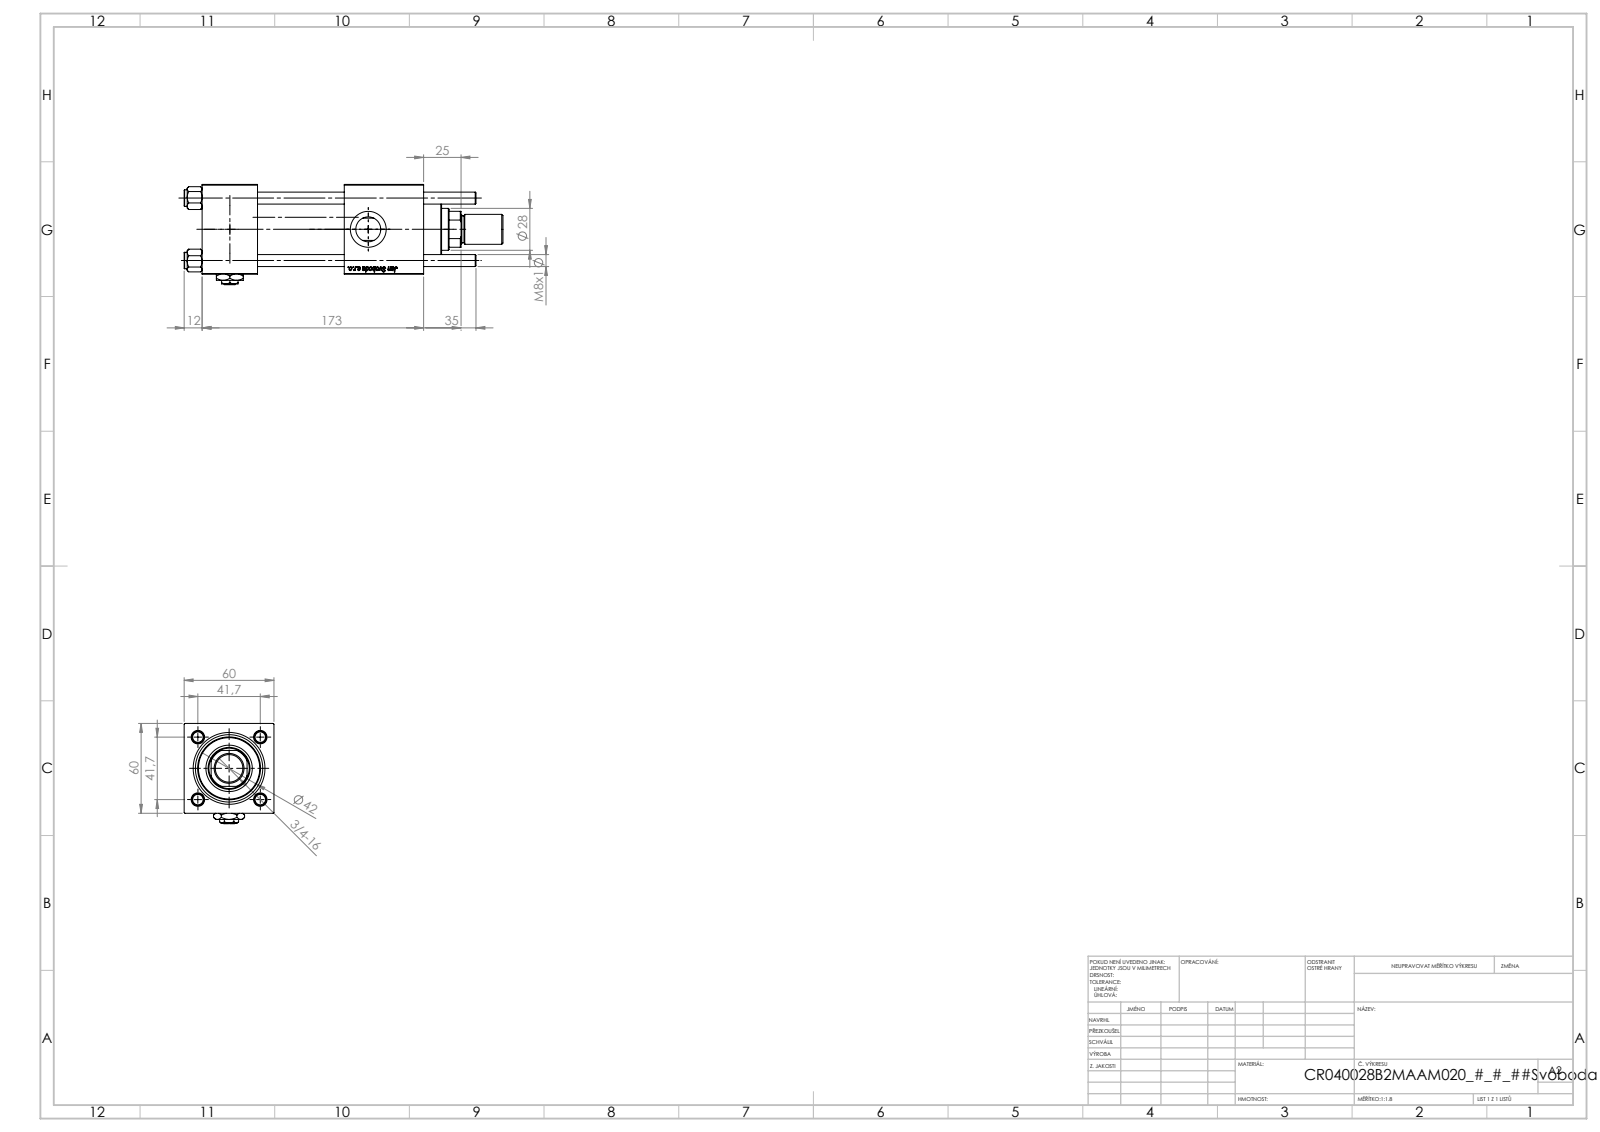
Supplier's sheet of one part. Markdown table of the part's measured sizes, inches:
| quantity | value |
| --- | --- |
| part name | Zatka_pro_OIL_PORT; V215CR_VCP_B; ROD_END_AH; V215CR_B-1 (+3 more) |
| STEP written by | SolidWorks 2019 (CONFIG_CONTROL_DESIGN) |
| units | inches |
| bodies | 13 solids, 1226 faces (460 planar, 90 cylindrical, 676 other) |
| overall size | 8.386 × 2.638 × 2.362 |
| volume | 26.98 in³ |
| surface area | 192.4 in² |
| round holes (diameter × count) | 0.315 × 4, 0.276 × 2, 0.656 × 2, 0.945 × 2, 0.63 × 1, 0.728 × 1, 1.102 × 1, 1.22 × 1, 1.575 × 1, 1.772 × 1 |
| round bosses / shafts (diameter × count) | 0.433 × 4, 1.811 × 1, 1.654 × 1, 0.787 × 1, 0.709 × 1 |
| partial cylindrical surfaces (radius × count) | 0.531 × 1 |
| main face-to-face distances | 2.362, 1.457, 2.283, 3.74, 2.087, 4.697, 3.24, 0.957, 5.827, 4.37 |
| hole center spacings | 1.161, 1.642, 2.322 |
